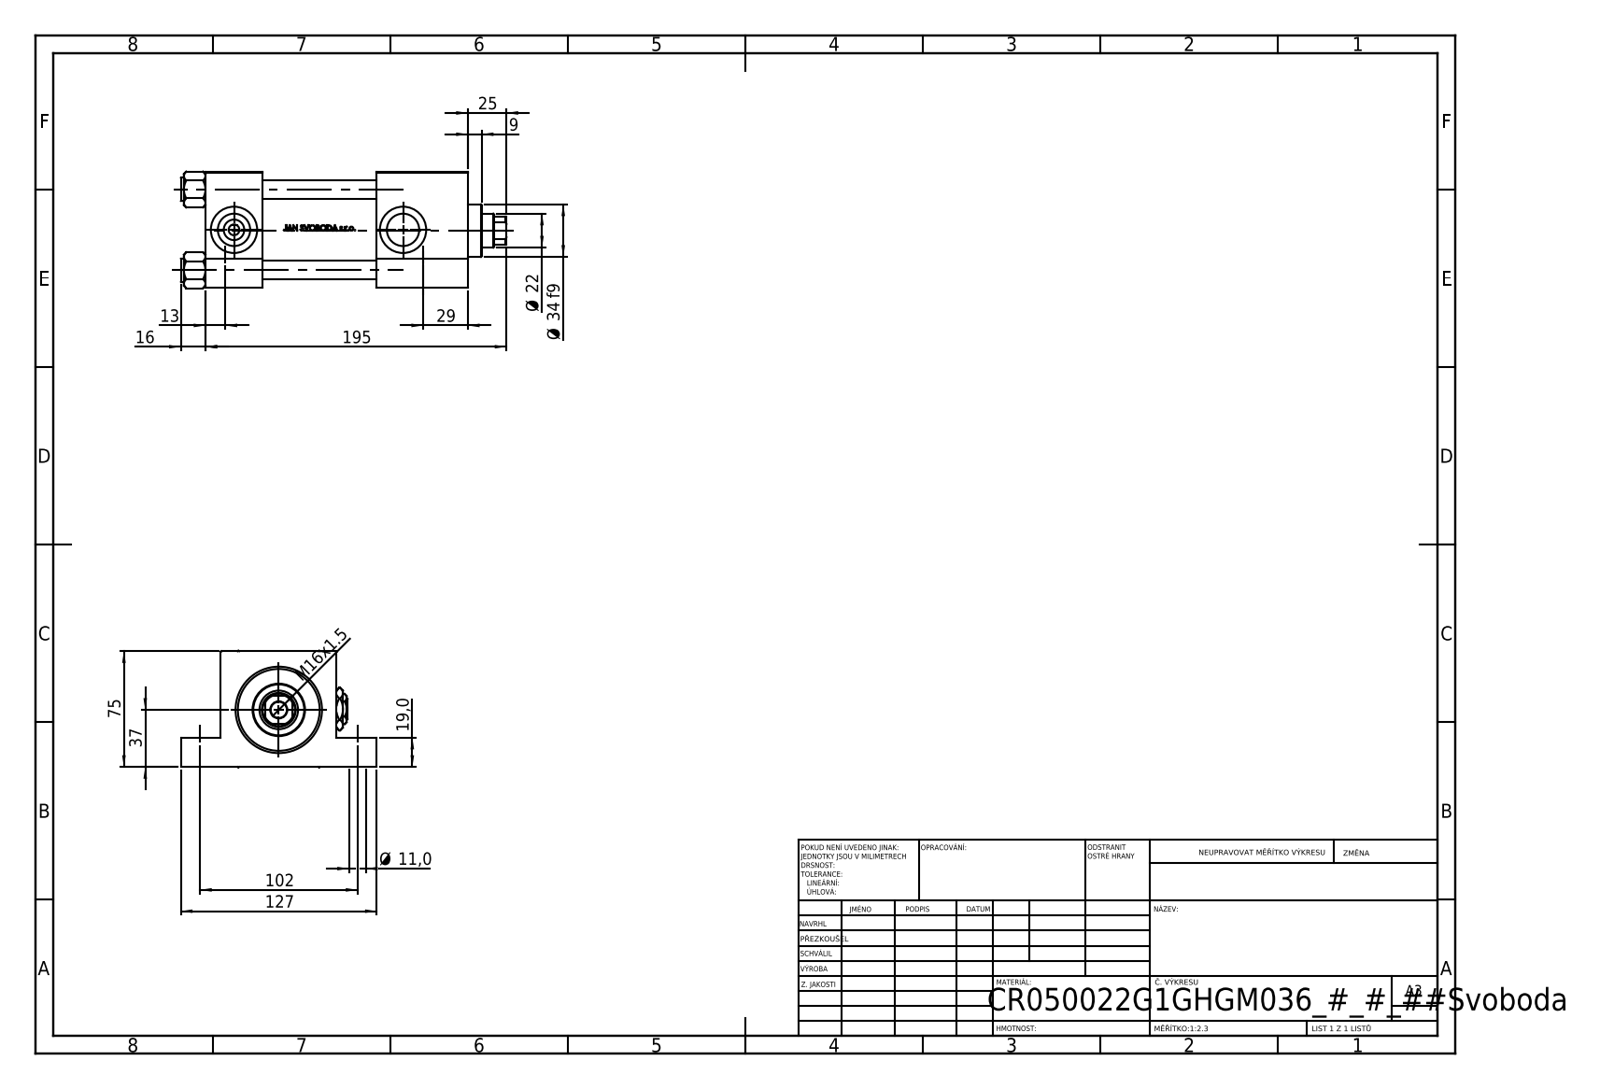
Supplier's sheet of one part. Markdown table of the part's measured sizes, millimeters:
| quantity | value |
| --- | --- |
| part name | V215CR_VCP_G; Zatka_pro_OIL_PORT; NUT_M5_G; V215CR_G_TYCINKA (+2 more) |
| STEP written by | SolidWorks 2019 (CONFIG_CONTROL_DESIGN) |
| units | millimeters |
| bodies | 12 solids, 1134 faces (454 planar, 128 cylindrical, 552 other) |
| overall size | 211 × 127 × 75.54 |
| volume | 773 716 mm³ |
| surface area | 170 150 mm² |
| round holes (diameter × count) | 11 × 4, 12 × 4, 7 × 2, 20.96 × 2, 30 × 2, 10.5 × 1, 22 × 1, 25 × 1, 41 × 1, 50 × 1, 53 × 1 |
| round bosses / shafts (diameter × count) | 15 × 4, 56 × 1, 34 × 1 |
| partial cylindrical surfaces (radius × count) | 10.5 × 1 |
| main face-to-face distances | 75, 37, 170, 133, 19, 56, 111, 74, 59, 26 |
| hole center spacings | 52.3, 36.63, 37.34, 73.96, 102, 128, 163.67, 109.5 |
